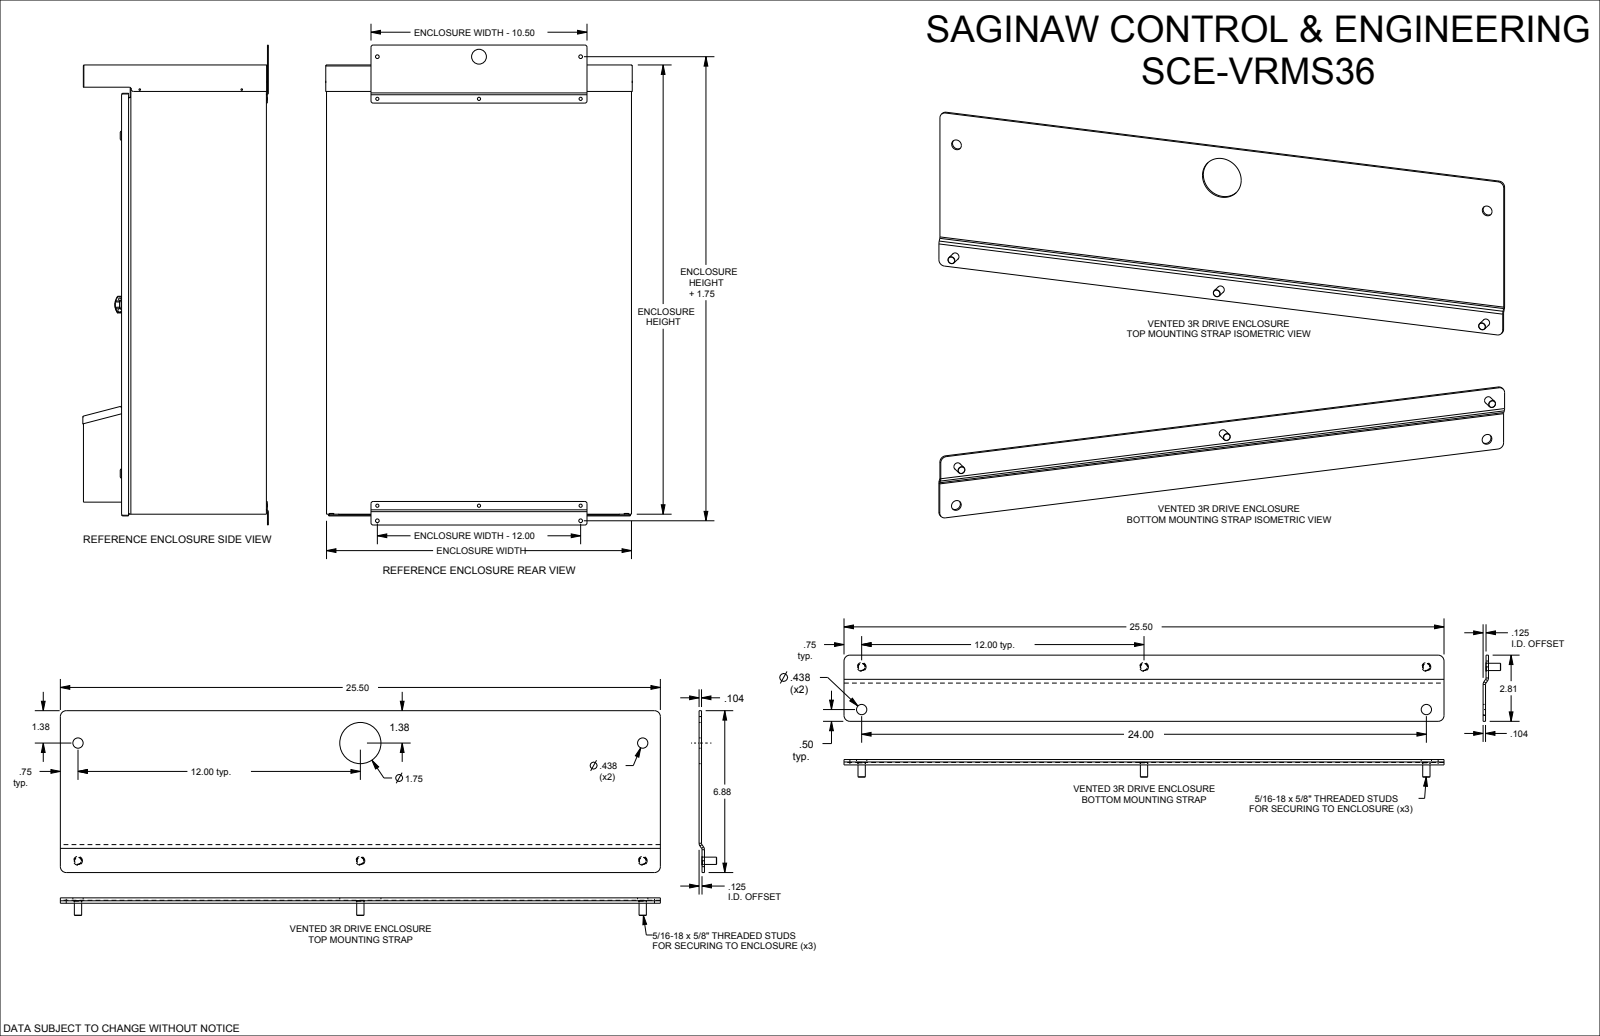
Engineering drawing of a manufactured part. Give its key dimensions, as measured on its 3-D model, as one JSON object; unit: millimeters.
{"part_name": "SCE-VRMS36", "step_written_by": "SolidWorks 2019 (CONFIG_CONTROL_DESIGN)", "units": "millimeters", "bodies": {"solids": 14, "faces": 347, "planar": 86, "cylindrical": 81, "other": 180}, "overall_size": [647.7, 320.7, 18.9], "volume_mm3": 427400, "surface_area_mm2": 333400, "round_holes": [[7.9, 6], [11.1, 4], [44.5, 1]], "round_bosses_or_shafts": [[9.6, 6], [7.9, 6]], "partial_cylinders_radius": [[0.3, 36], [6.4, 8], [2.5, 4], [5.2, 4]], "face_to_face_distances": [2.6, 3.2, 5.8, 0.5, 320.7, 174.6, 249.3, 74.7, 146.1, 71.4], "hole_center_spacings": [304.8, 320.8, 330.2, 380.1, 609.6, 100.1, 127, 227.1]}
